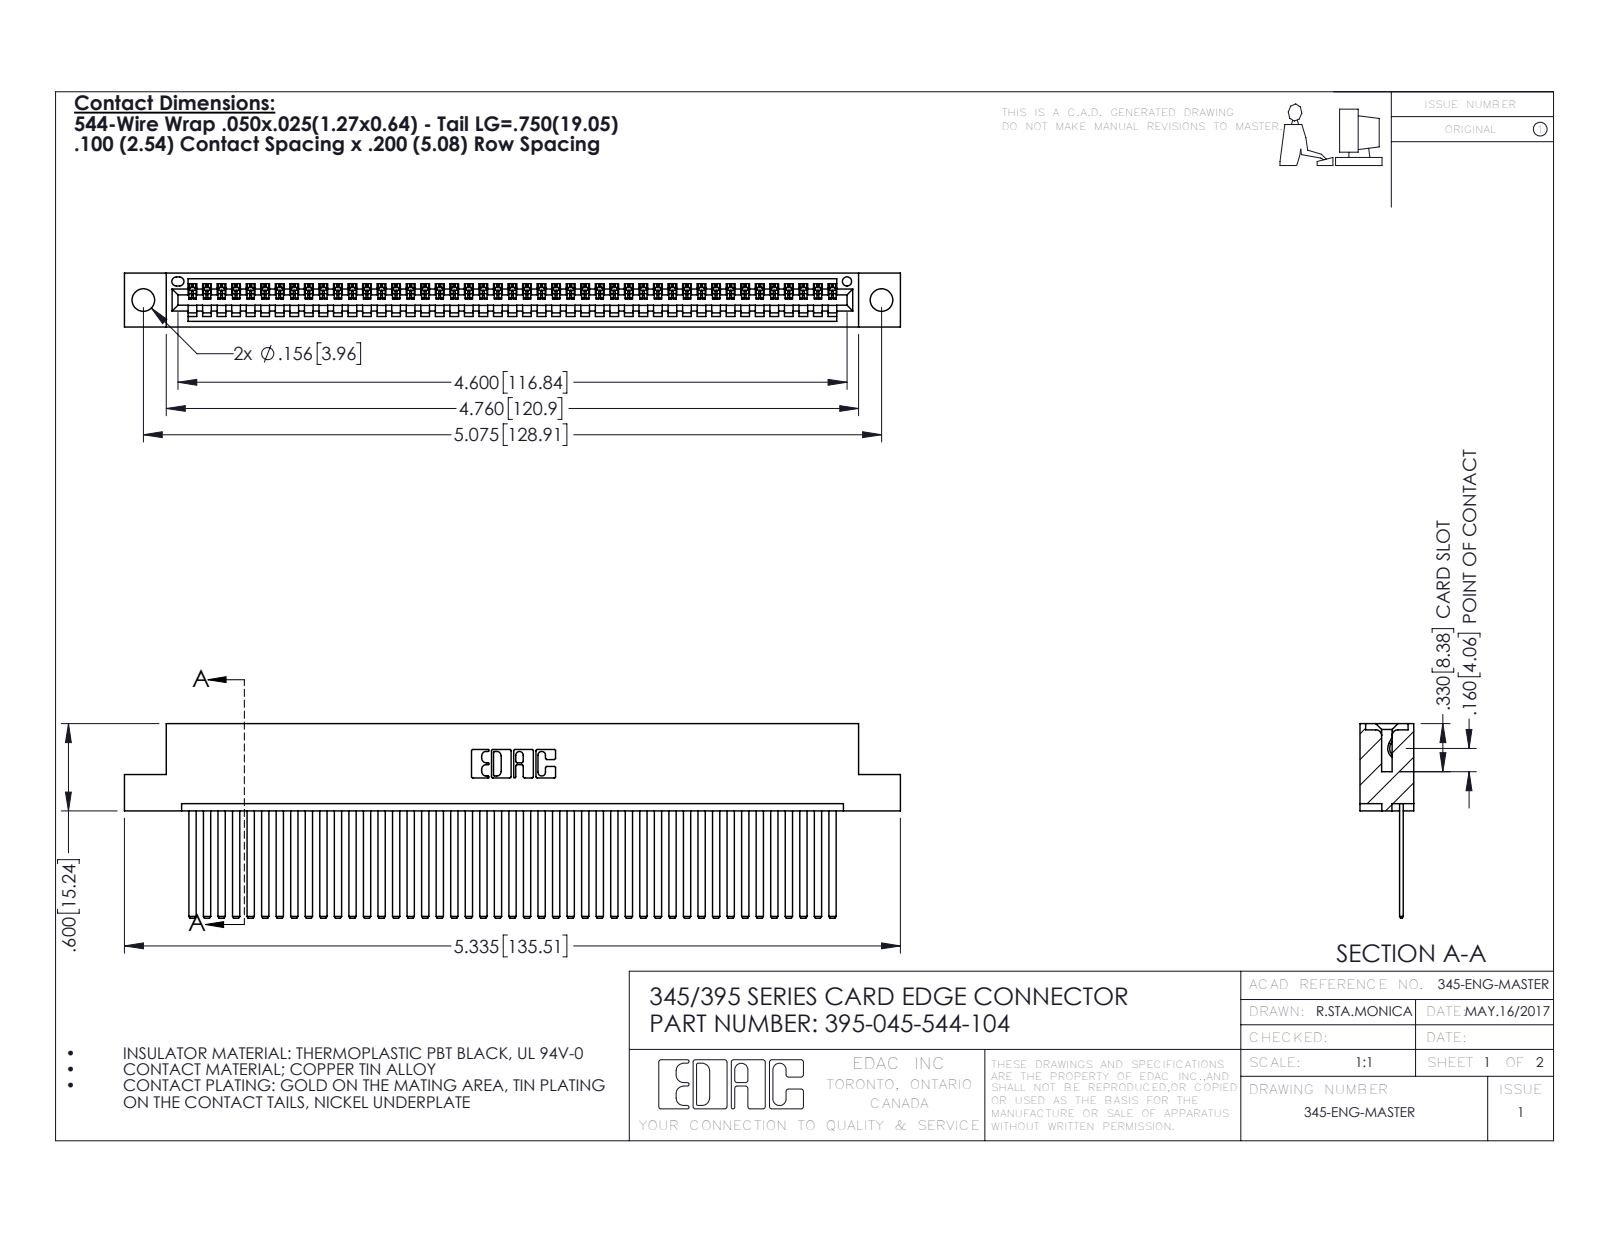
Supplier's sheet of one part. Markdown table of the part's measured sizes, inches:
| quantity | value |
| --- | --- |
| part name | 345-292-001_345-293-144; 395-045-544-104; 345 Part_Flush Mounting Lugs - 0.156 Dia-TH |
| STEP written by | SolidWorks 2016 (CONFIG_CONTROL_DESIGN) |
| units | inches |
| bodies | 46 solids, 2466 faces (1700 planar, 766 cylindrical, 0 other) |
| overall size | 5.335 × 1.337 × 0.37 |
| volume | 0.813 in³ |
| surface area | 29.65 in² |
| round holes (diameter × count) | 0.156 × 2, 0.064 × 1 |
| partial cylindrical surfaces (radius × count) | 0.006 × 90, 0.01 × 22, 0.007 × 6, 0.031 × 6, 0.026 × 3, 0.031 × 2, 0.04 × 2, 0.014 × 1 |
| main face-to-face distances | 0.072, 0.298, 0.025, 0.098, 0.272, 0.37, 0.2, 0.225, 0.149, 0.072 |
| hole center spacings | 0.27, 4.839, 5.075 |
